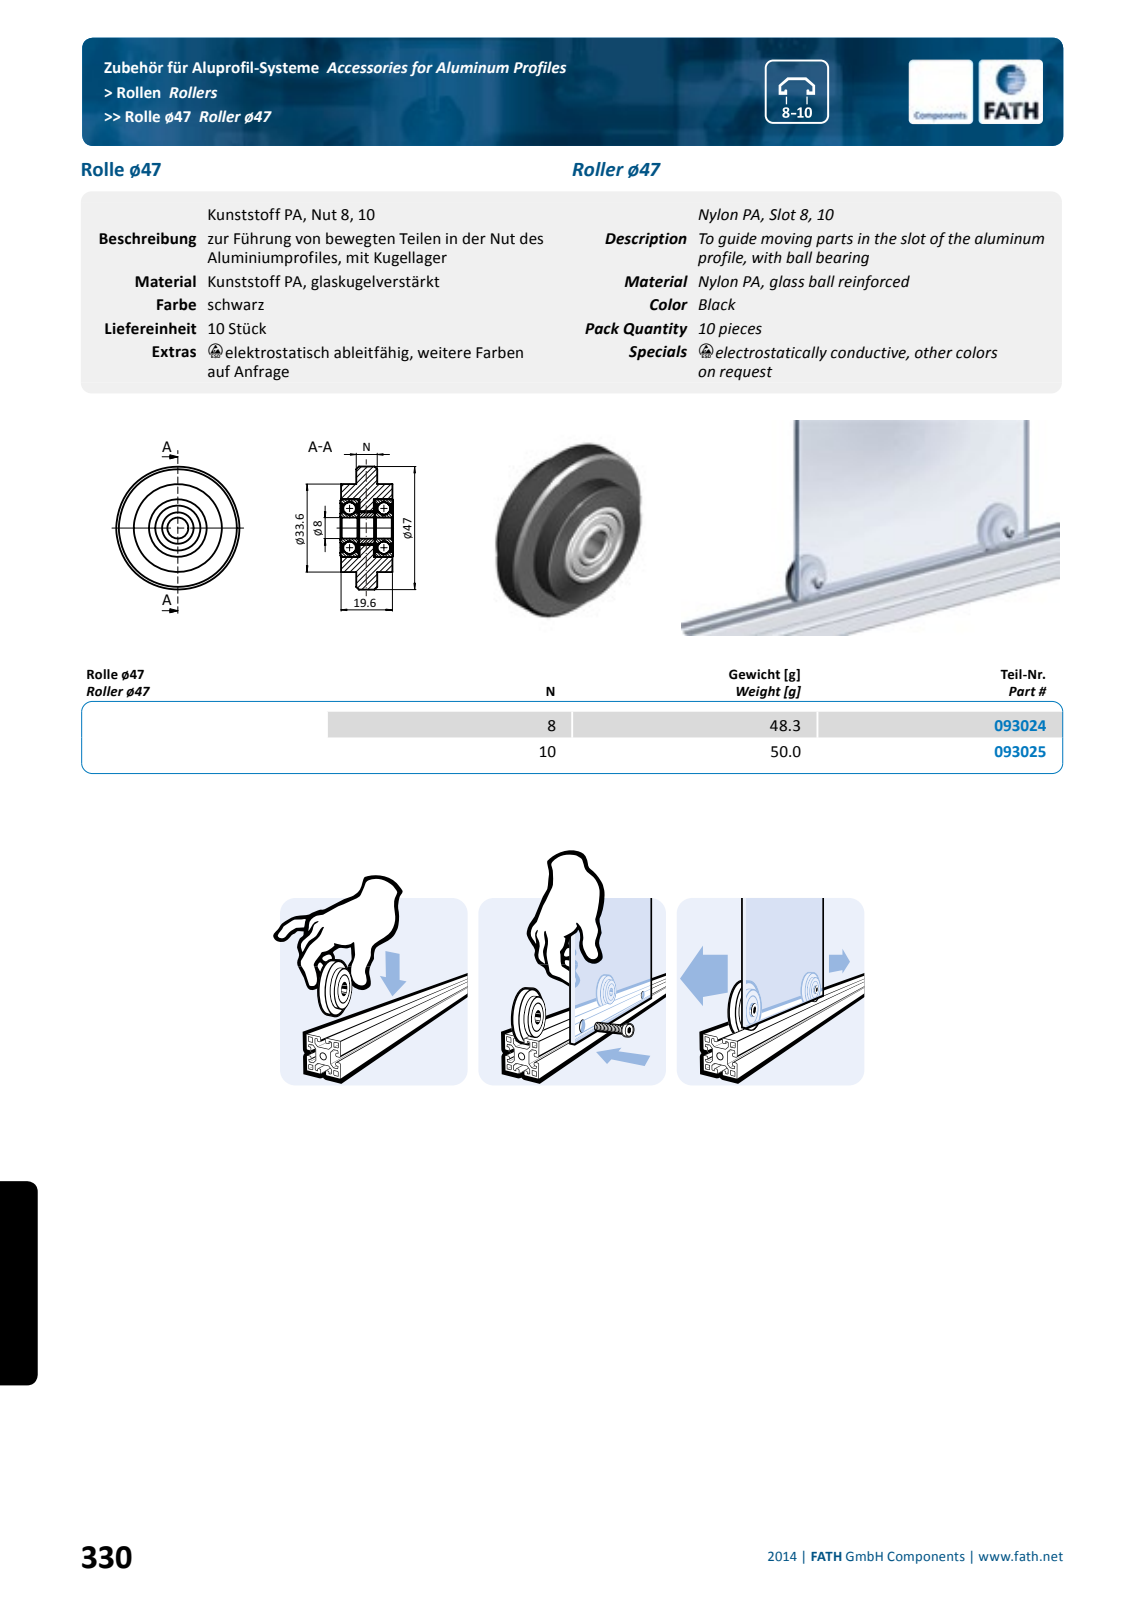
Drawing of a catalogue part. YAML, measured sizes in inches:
part_name: "fath_093025_1; fath_093025_2; fath_093025_3; fath_093025_4 (+8 more)"
step_written_by: "Spatial InterOp 3D (automotive_design)"
units: inches
bodies: {solids: 14, faces: 172, planar: 24, cylindrical: 56, other: 92}
overall_size: [1.89, 1.89, 0.791]
volume: 1.419
surface_area: 18.99
round_holes:
  - {diameter: 0.315, count: 1}
  - {diameter: 0.319, count: 1}
  - {diameter: 0.512, count: 1}
  - {diameter: 0.709, count: 1}
  - {diameter: 0.866, count: 1}
round_bosses_or_shafts:
  - {diameter: 1.89, count: 1}
  - {diameter: 1.323, count: 1}
  - {diameter: 0.472, count: 1}
face_to_face_distances: [0.189, 0.579, 0.39, 0.488, 0.516, 0.24, 0.768, 0.28, 0.091, 0.299]
